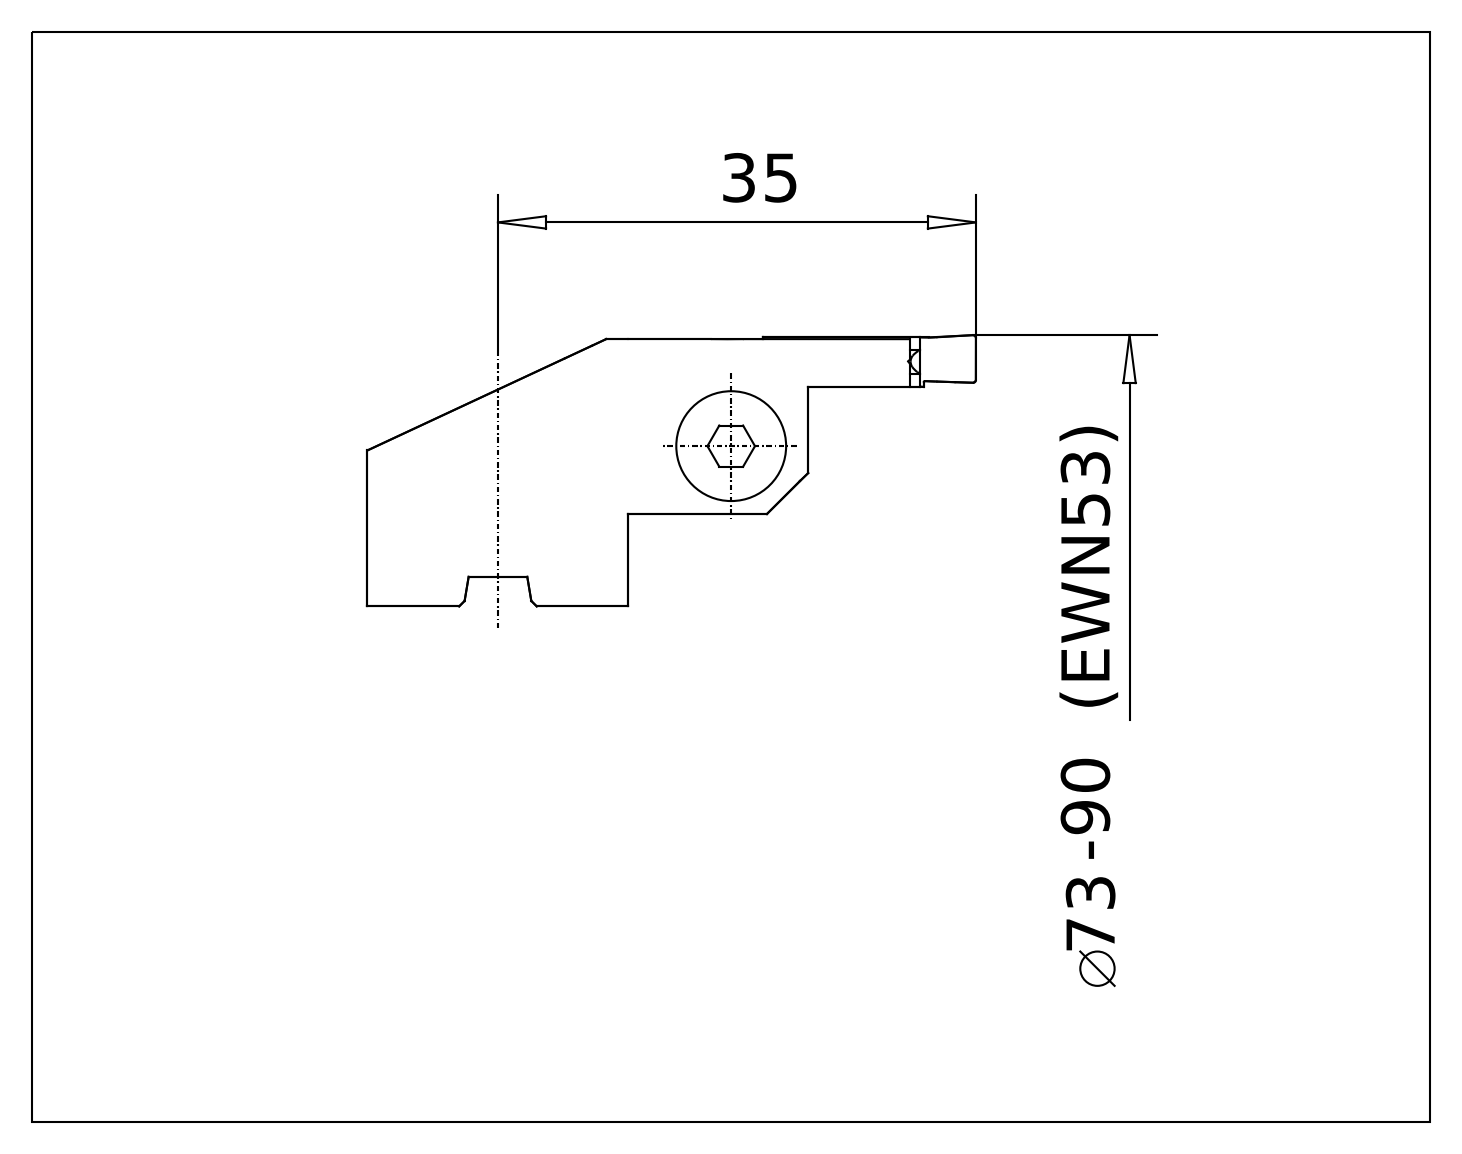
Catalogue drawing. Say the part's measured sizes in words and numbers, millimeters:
The part is named "626.945 Kaiser ENH 52 S4 73-90 R|690.183 Kaiser ETL M5x12A;Verrundung1; 626.945 Kaiser ENH 52 S4 73-90 R|958.425 Kaiser NP 4250 P20C_Einstechplatte 4mm;NONE; 626.945 Kaiser ENH 52 S4 73-90 R|626.945 Kaiser ENH 52 S4 73-90 R;Fase30". Its 3-D file was written by "ACIS (automotive_design)". It is 3 solids with 133 faces: 82 planar, 39 cylindrical and 12 other. Overall it measures 44.86 by 19.76 by 19 millimeters. Its volume is 6 515 cubic millimeters and its surface area 4 161 square millimeters. Round holes: 1 of diameter 4.2, 1 of diameter 5.05, 1 of diameter 5.2, 1 of diameter 8.9, 1 of diameter 9. Round bosses or shafts: 1 of diameter 19, 1 of diameter 8.5, 1 of diameter 5. Partial cylindrical surfaces (rounded edges, fillets, slot ends): 4 of radius 0.2, 2 of radius 0.1, 2 of radius 1.4, 2 of radius 1.63, 1 of radius 1.26, 1 of radius 8, 1 of radius 44.5. The main face-to-face distances are 1.61, 16, 1.99, 3.6, 2.15, 9.97, 3.5, 3.51, 1.35, 12. The hole center spacings are 10.77.
